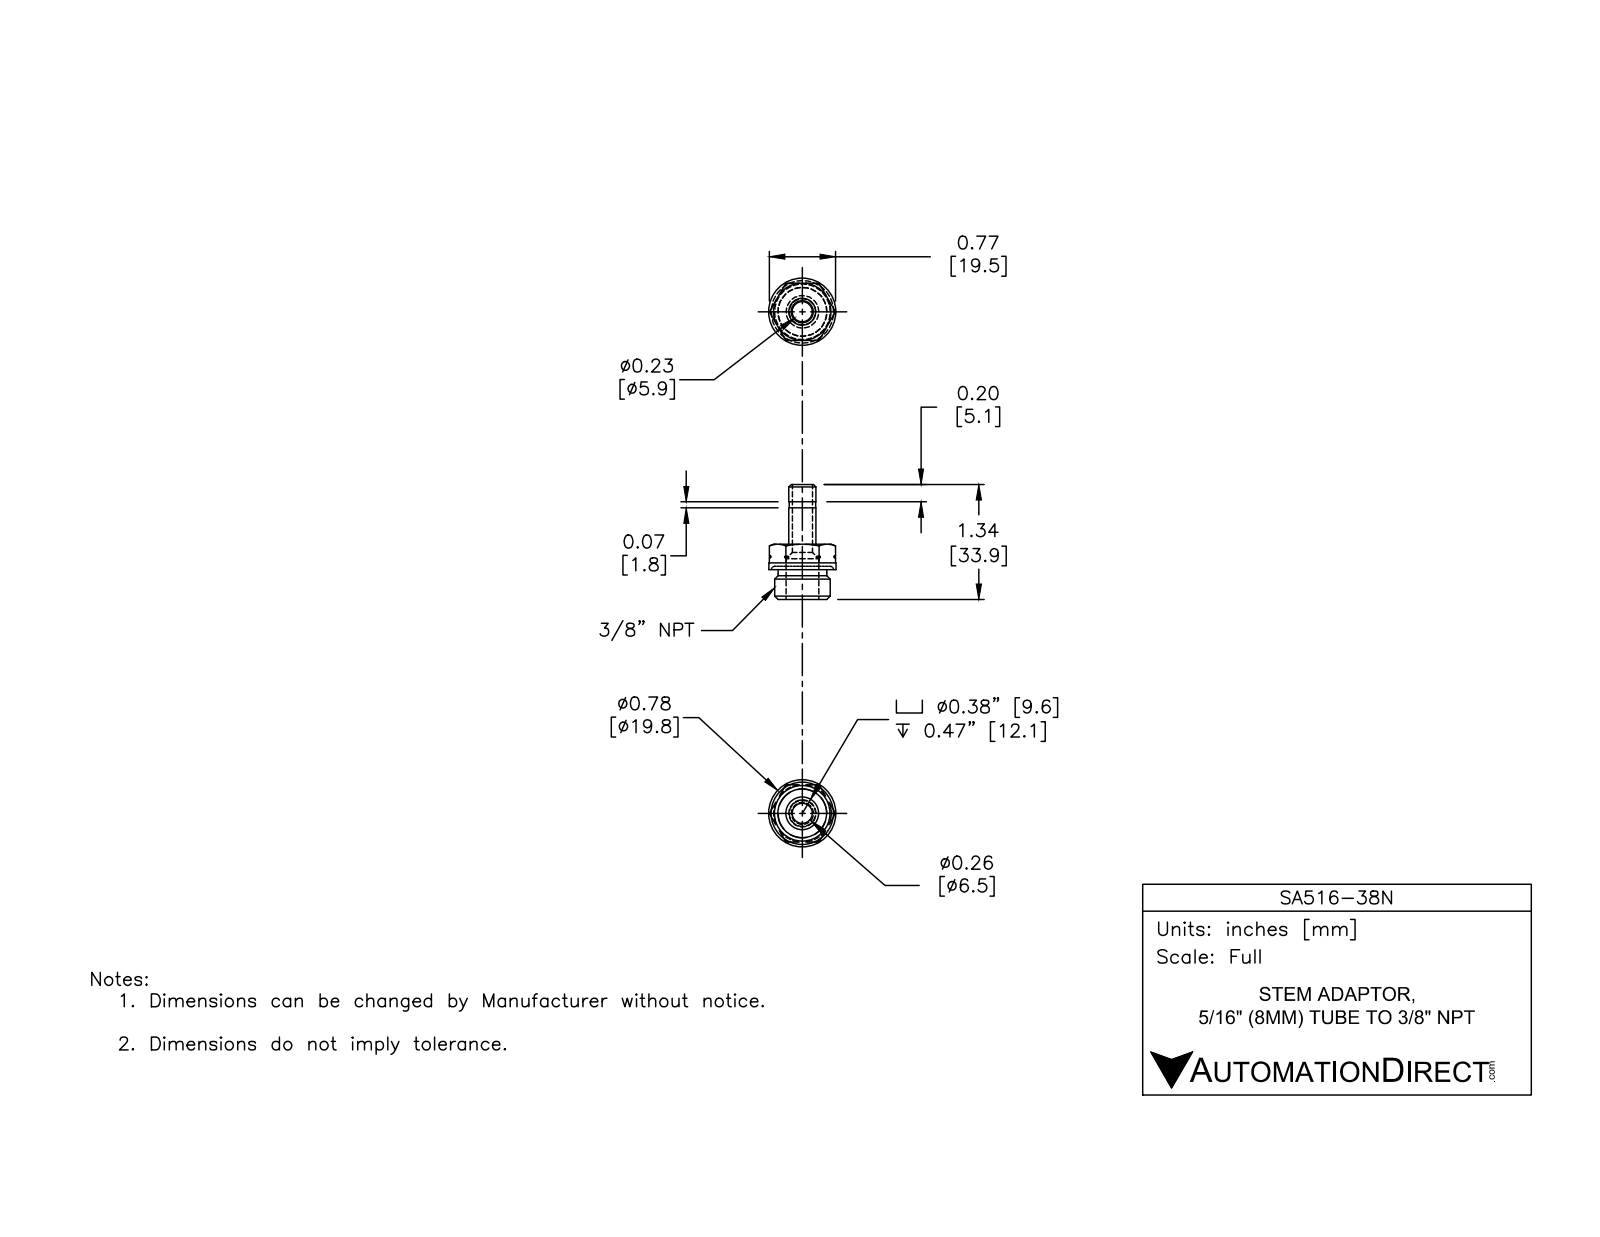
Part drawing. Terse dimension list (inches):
name: SA516-38N
written by: SolidWorks 2015 (CONFIG_CONTROL_DESIGN)
unit: in
bodies: 2 solids, 65 faces (13 planar, 22 cylindrical, 30 other)
size: 1.335 × 0.778 × 0.778
volume: 0.196 in³; area: 4.628 in²
holes: 1× ⌀0.232, 1× ⌀0.378
bosses: 1× ⌀0.778, 1× ⌀0.646, 1× ⌀0.567, 1× ⌀0.315, 1× ⌀0.305
rounds: 1× R0.37
face distances: 0.665, 0.295, 0.346, 0.642, 0.425, 0.079, 0.217, 1.335, 0.989, 0.91
